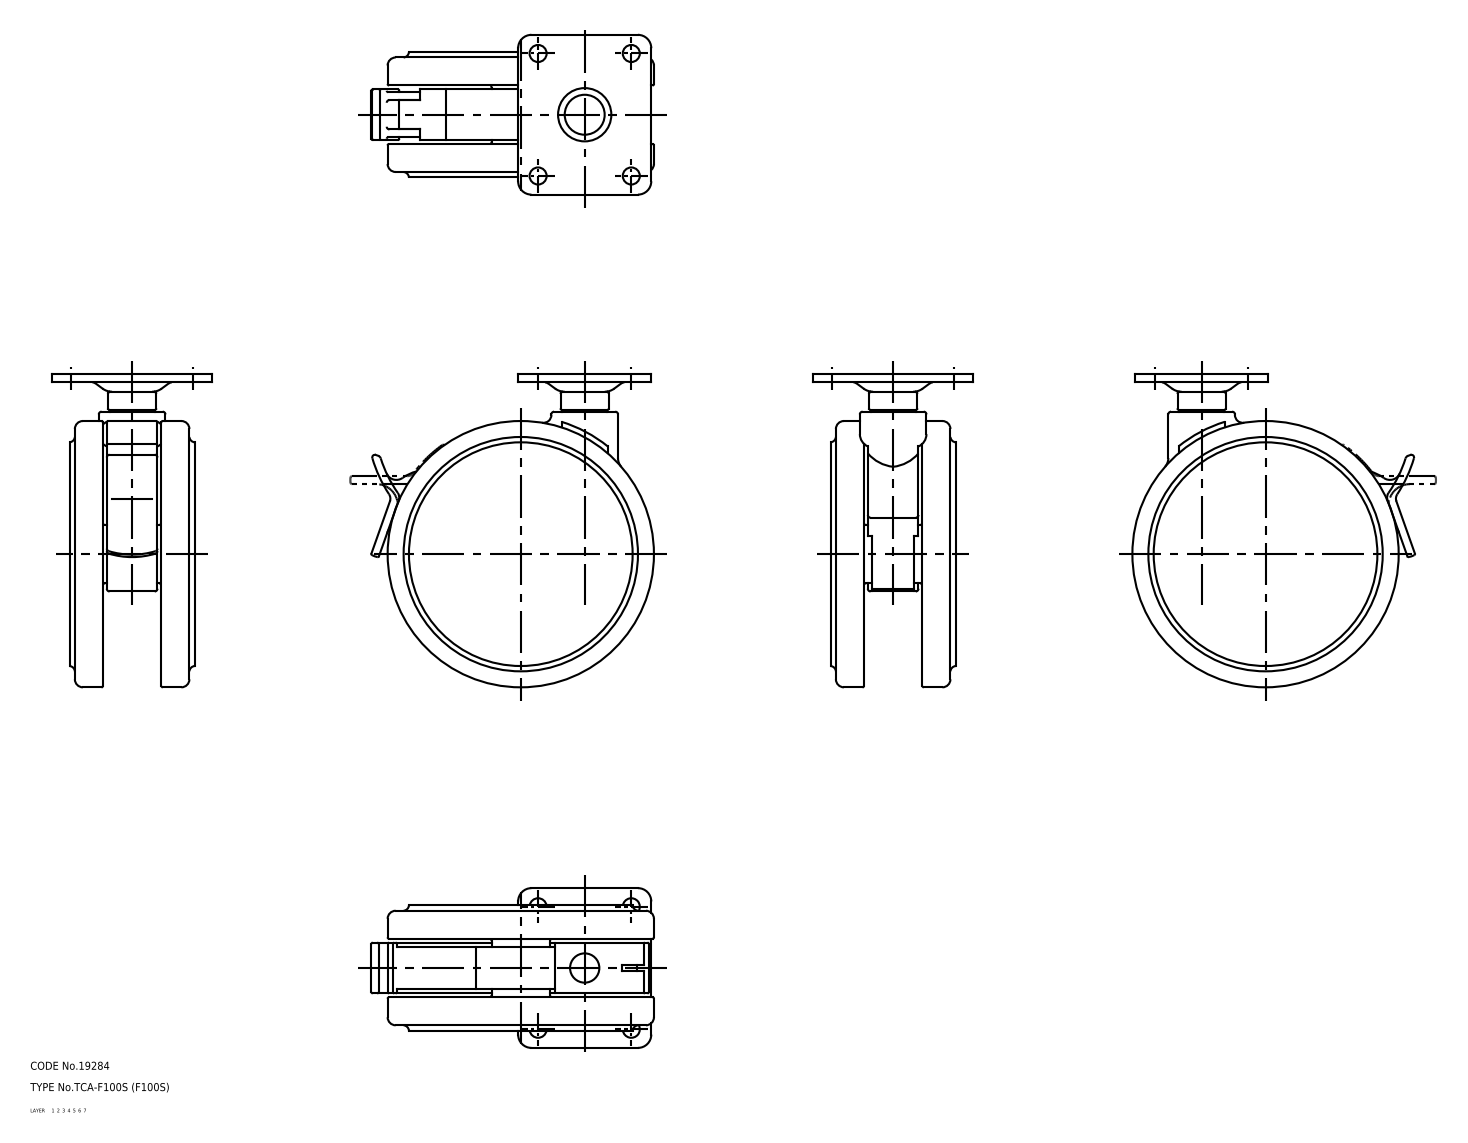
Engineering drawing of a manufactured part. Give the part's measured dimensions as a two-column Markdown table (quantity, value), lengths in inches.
| quantity | value |
| --- | --- |
| part name | 67124777; 67124790; 67124803; 67124816 (+2 more) |
| STEP written by | CADfix (AUTOMOTIVE_DESIGN) |
| units | inches |
| bodies | 6 solids, 276 faces (0 planar, 0 cylindrical, 276 other) |
| overall size | 4.626 × 4.178 × 2.362 |
| volume | 14.7 in³ |
| surface area | 104.8 in² |
